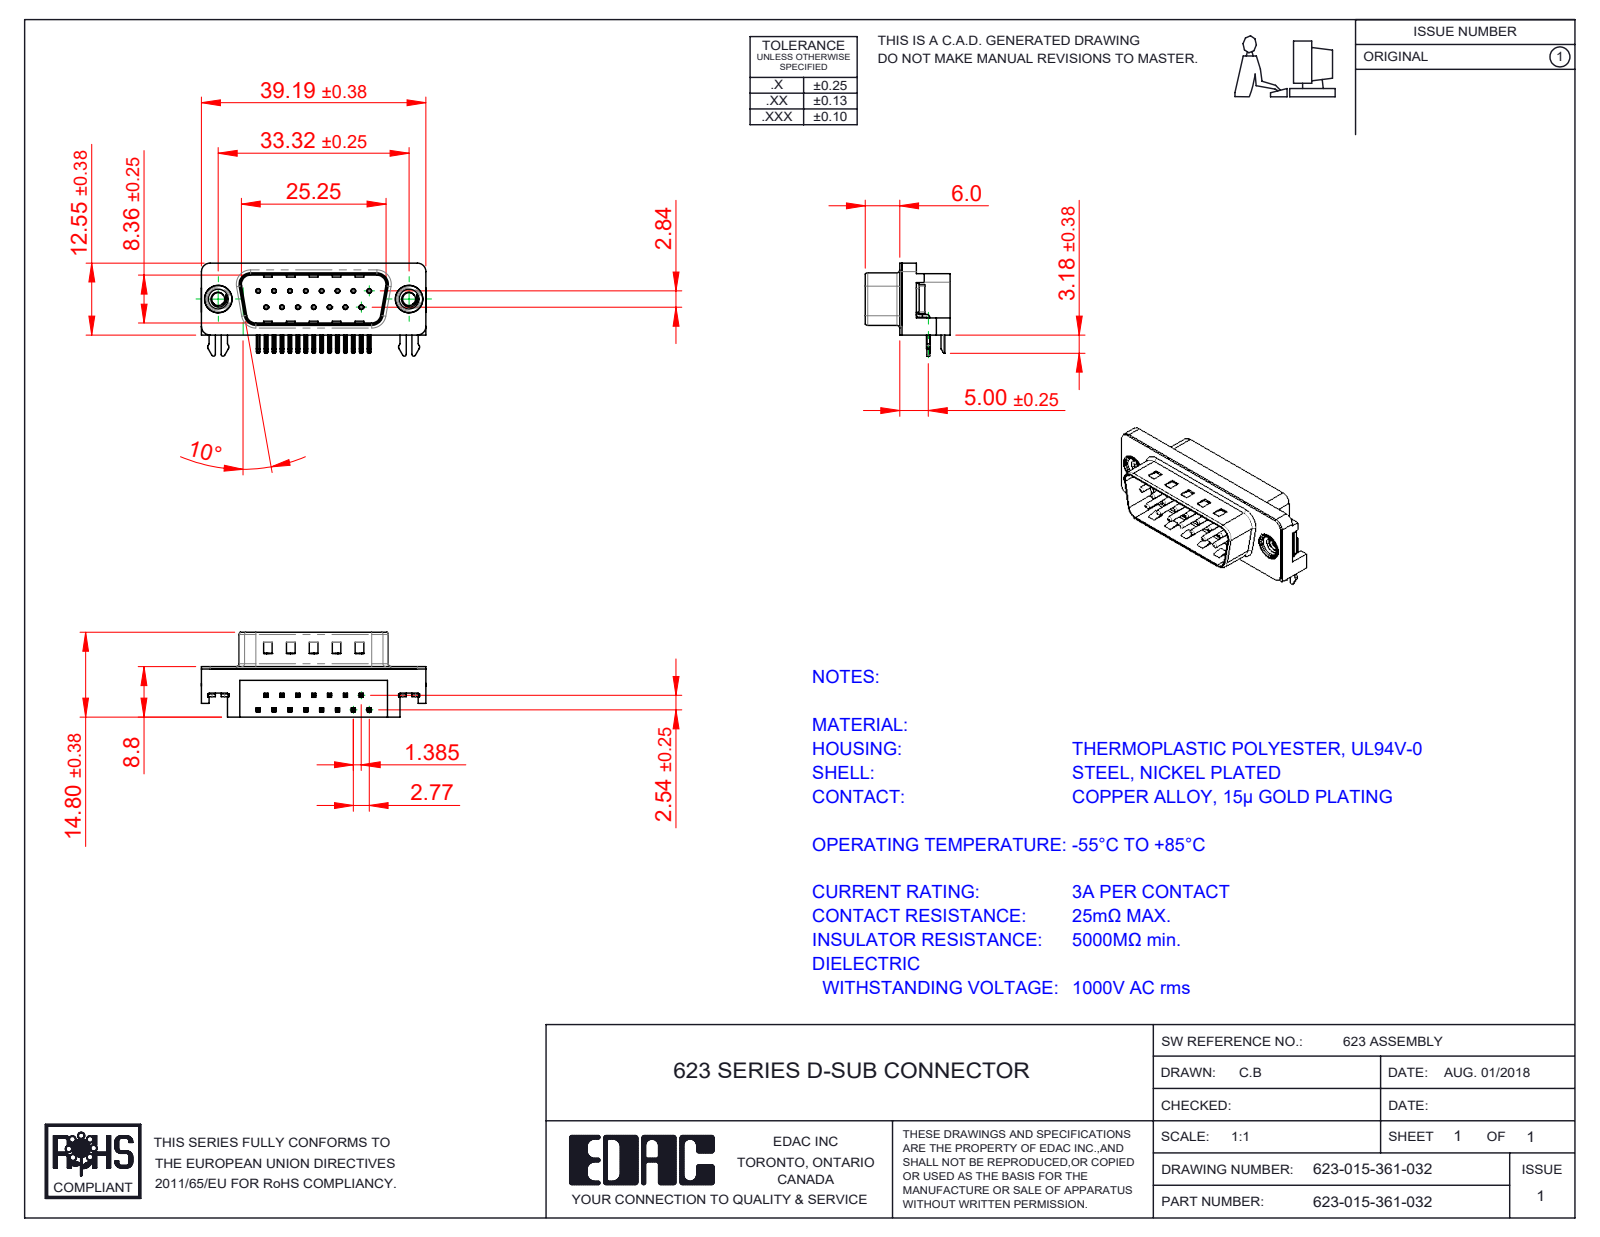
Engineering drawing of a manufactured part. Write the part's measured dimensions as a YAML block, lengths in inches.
part_name: "623 2 Prong Board Lock; 623 Contact Top; 623 Housing_15 Socket; 623 4-40 Threaded Rivet (+3 more)"
step_written_by: "SolidWorks 2016 (CONFIG_CONTROL_DESIGN)"
units: inches
bodies: {solids: 21, faces: 1499, planar: 921, cylindrical: 439, other: 139}
overall_size: [1.544, 0.64, 0.583]
volume: 0.203
surface_area: 7.668
round_holes:
  - {diameter: 0.014, count: 15}
  - {diameter: 0.031, count: 15}
  - {diameter: 0.089, count: 2}
  - {diameter: 0.157, count: 2}
  - {diameter: 0.189, count: 2}
  - {diameter: 0.197, count: 2}
round_bosses_or_shafts:
  - {diameter: 0.03, count: 15}
  - {diameter: 0.193, count: 2}
  - {diameter: 0.187, count: 2}
  - {diameter: 0.154, count: 2}
partial_cylinders:
  - {radius: 0.01, count: 68}
  - {radius: 0.005, count: 30}
  - {radius: 0.02, count: 14}
  - {radius: 0.039, count: 8}
  - {radius: 0.059, count: 6}
  - {radius: 0.013, count: 4}
  - {radius: 0.035, count: 4}
  - {radius: 0.063, count: 4}
face_to_face_distances: [0.016, 0.331, 0.083, 0.067, 0.412, 0.346, 0.428, 0.345, 0.232, 0.114]
hole_center_spacings: [0.124, 0.109, 0.218, 0.327, 0.436, 0.198, 0.198, 0.294]
